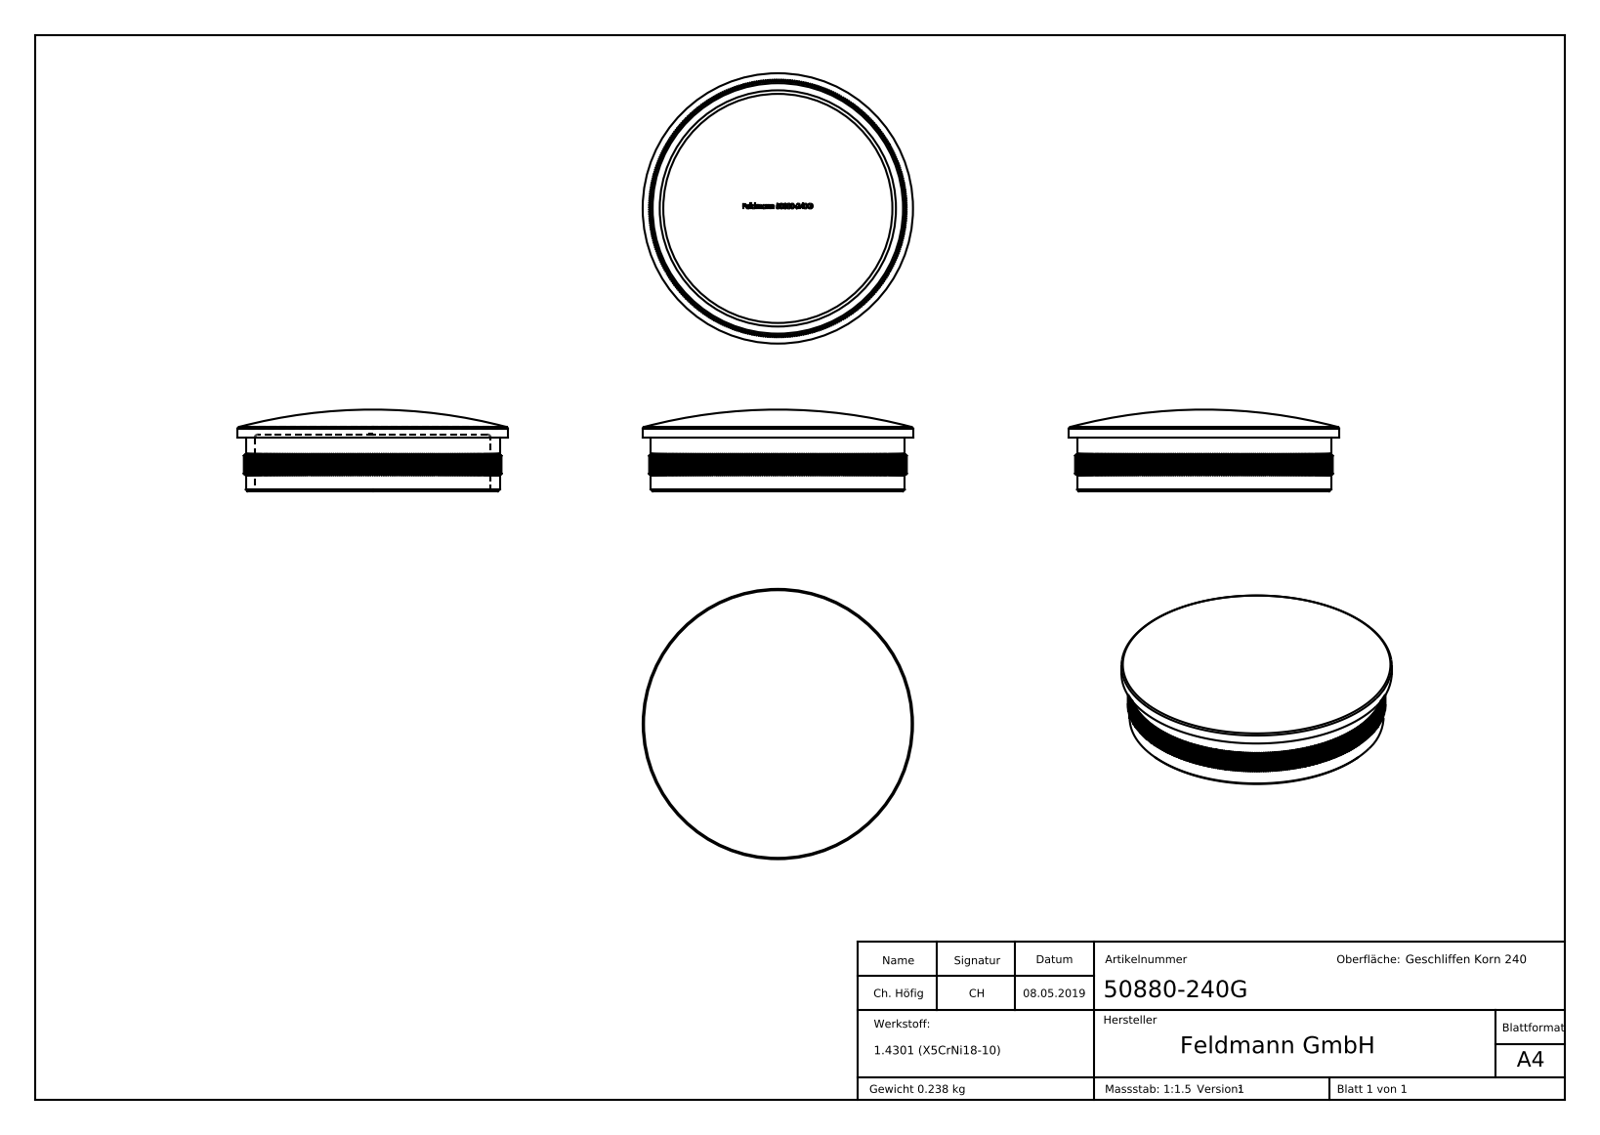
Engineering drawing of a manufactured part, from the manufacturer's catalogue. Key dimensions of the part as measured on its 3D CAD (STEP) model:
Part name (STEP PRODUCT): 50880-240G
STEP written by: SolidWorks 2015 (CONFIG_CONTROL_DESIGN)
Units: millimetres
Bodies: 1 solid, 2067 faces (839 planar, 368 cylindrical, 860 other)
Overall size (bounding box): 76.1 × 76.1 × 23
Volume: 30 078 mm³ · Surface area: 17 514 mm²
Round holes (diameter × count): ⌀66.5 ×1
Round bosses / shafts (diameter × count): ⌀76.1 ×1, ⌀71.5 ×1
Partial cylindrical surfaces — rounded edges, fillets, slot ends (radius × count): R36.2 ×1
Main face-to-face distances: 1, 15, 16, 35.75, 35.76, 35.74, 35.78, 35.77, 35.72, 35.73
